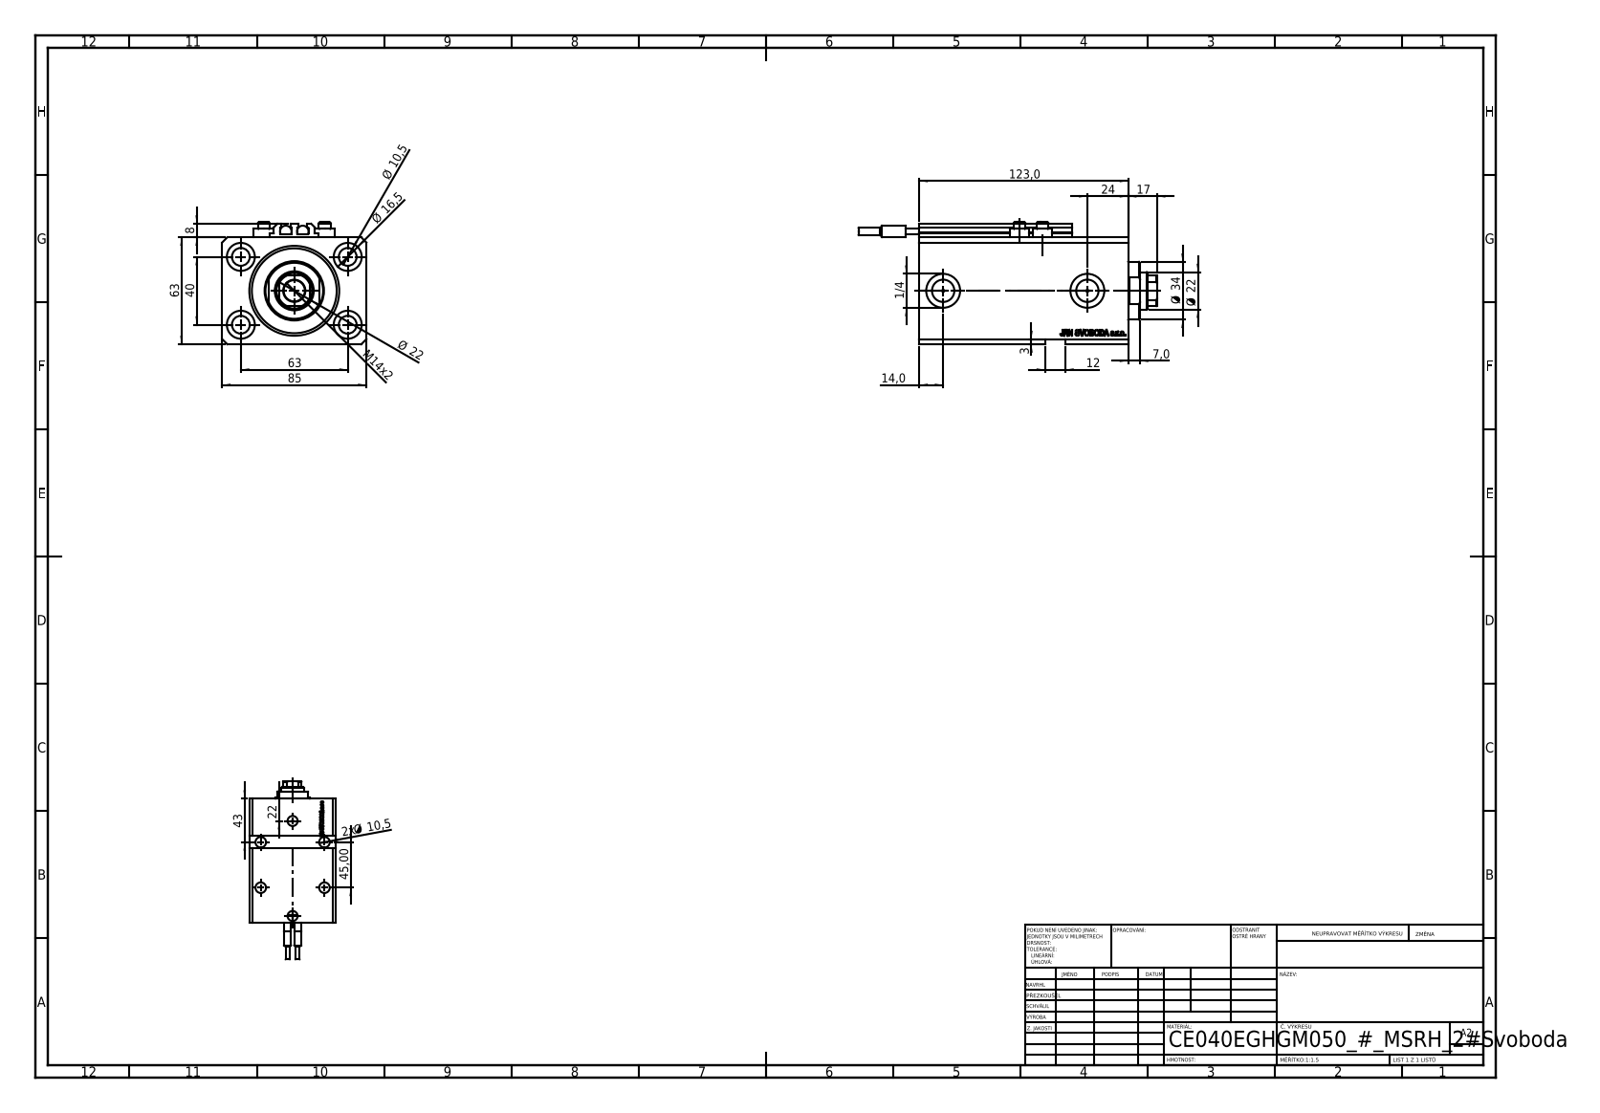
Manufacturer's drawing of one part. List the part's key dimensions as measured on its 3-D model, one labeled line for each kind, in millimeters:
Part name (STEP PRODUCT): ALLEN BOLT V250CE; V250CE_VC_E; SWITCH_V250CE; V250CE_E_Body (+1 more)
STEP written by: SolidWorks 2019 (CONFIG_CONTROL_DESIGN)
Units: millimetres
Bodies: 10 solids, 1159 faces (567 planar, 158 cylindrical, 434 other)
Overall size (bounding box): 176 × 85 × 72
Volume: 560 212 mm³ · Surface area: 122 077 mm²
Round holes (diameter × count): ⌀10.5 ×8, ⌀1.25 ×4, ⌀4 ×4, ⌀16.5 ×4, ⌀10 ×2, ⌀13.16 ×2, ⌀20 ×2, ⌀12.5 ×1, ⌀22 ×1, ⌀40 ×1, ⌀53 ×1
Round bosses / shafts (diameter × count): ⌀11.6 ×4, ⌀7 ×4, ⌀6.8 ×2, ⌀6.5 ×2, ⌀4 ×2, ⌀34 ×1
Partial cylindrical surfaces — rounded edges, fillets, slot ends (radius × count): R0.2 ×10, R10.5 ×1
Main face-to-face distances: 63, 85, 123, 17, 106, 3, 11.4, 94.6, 111.6, 65
Hole centre spacings: 37.31, 63, 13.6, 15.4, 24.96, 27.54, 33.62, 36
